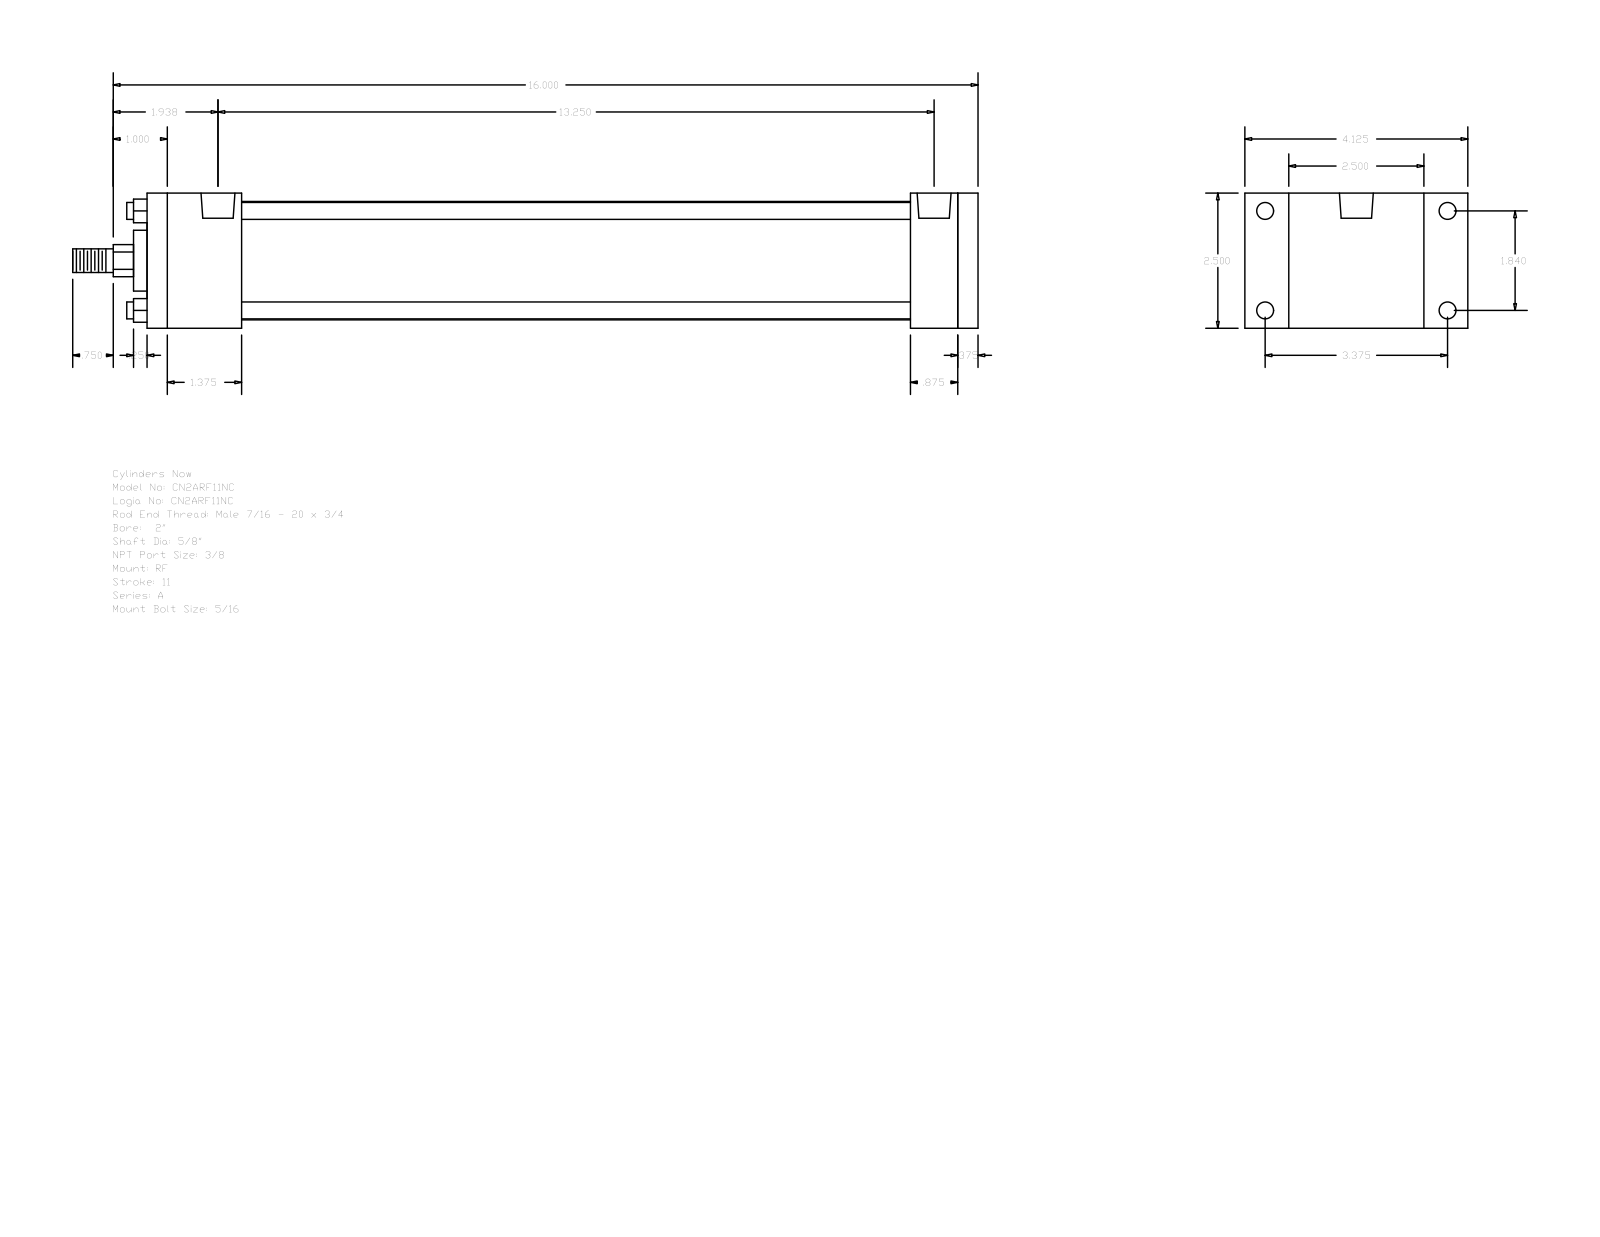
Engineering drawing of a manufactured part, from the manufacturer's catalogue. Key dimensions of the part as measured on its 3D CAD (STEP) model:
Part name (STEP PRODUCT): A_RF__0200_0.625
STEP written by: GSSL Pune (CONFIG_CONTROL_DESIGN)
Units: millimetres
Bodies: 0 solids, 92 faces (64 planar, 28 cylindrical, 0 other)
Overall size (bounding box): 425.45 × 104.78 × 63.5
Round holes (diameter × count): ⌀5.56 ×4, ⌀7.94 ×4, ⌀15.93 ×2
Round bosses / shafts (diameter × count): ⌀7.94 ×4, ⌀55.63 ×1, ⌀28.57 ×1, ⌀15.88 ×1, ⌀11.11 ×1
Partial cylindrical surfaces — rounded edges, fillets, slot ends (radius × count): R7.54 ×1
Main face-to-face distances: 63.5, 390.52, 381, 9.52, 44.45, 336.55, 346.07, 358.77, 314.32, 22.23
Hole centre spacings: 46.74, 85.72, 97.63, 328.6, 3.97, 3.98, 332.57, 332.58
